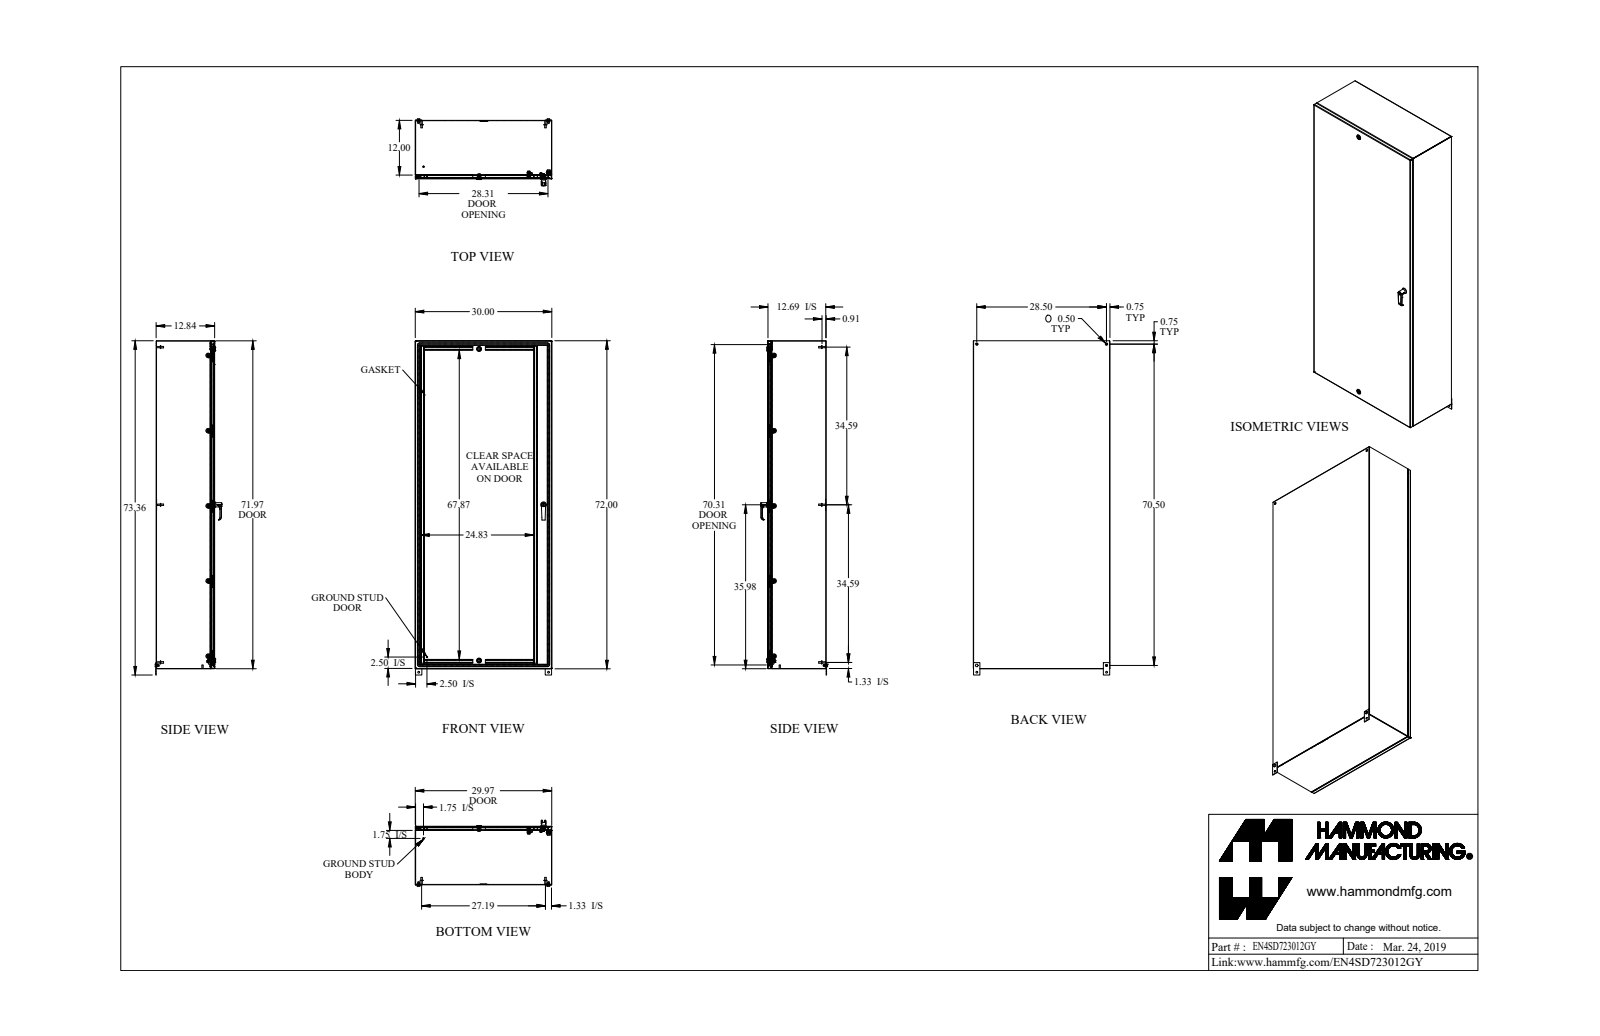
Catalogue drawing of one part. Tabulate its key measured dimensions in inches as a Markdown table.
| quantity | value |
| --- | --- |
| part name | EN4SD723012GY |
| STEP written by | SolidWorks 2018 (AUTOMOTIVE_DESIGN) |
| units | inches |
| bodies | 98 solids, 2429 faces (1159 planar, 890 cylindrical, 380 other) |
| overall size | 73.363 × 30 × 14.693 |
| volume | 573.5 in³ |
| surface area | 16 119 in² |
| round holes (diameter × count) | 0.176 × 10, 0.196 × 6, 0.25 × 5, 0.265 × 5, 0.413 × 5, 0.256 × 4, 0.313 × 4, 0.39 × 4, 0.394 × 4, 0.5 × 4, 0.232 × 2, 0.307 × 2 |
| round bosses / shafts (diameter × count) | 0.25 × 11, 0.375 × 10, 0.156 × 10, 0.625 × 7, 0.313 × 6, 0.27 × 6, 1 × 5, 0.63 × 4 |
| partial cylindrical surfaces (radius × count) | 0.043 × 24, 0.062 × 19, 0.036 × 17, 0.108 × 17, 0.03 × 15, 0.125 × 14, 0.006 × 10, 0.094 × 10 |
| main face-to-face distances | 0.072, 12.765, 12.693, 12.837, 29.928, 29.856, 30, 71.928, 71.856, 72 |
| hole center spacings | 16.513, 28.5, 49.487, 1.5, 2.507, 13.313, 14.208, 15.267 |
